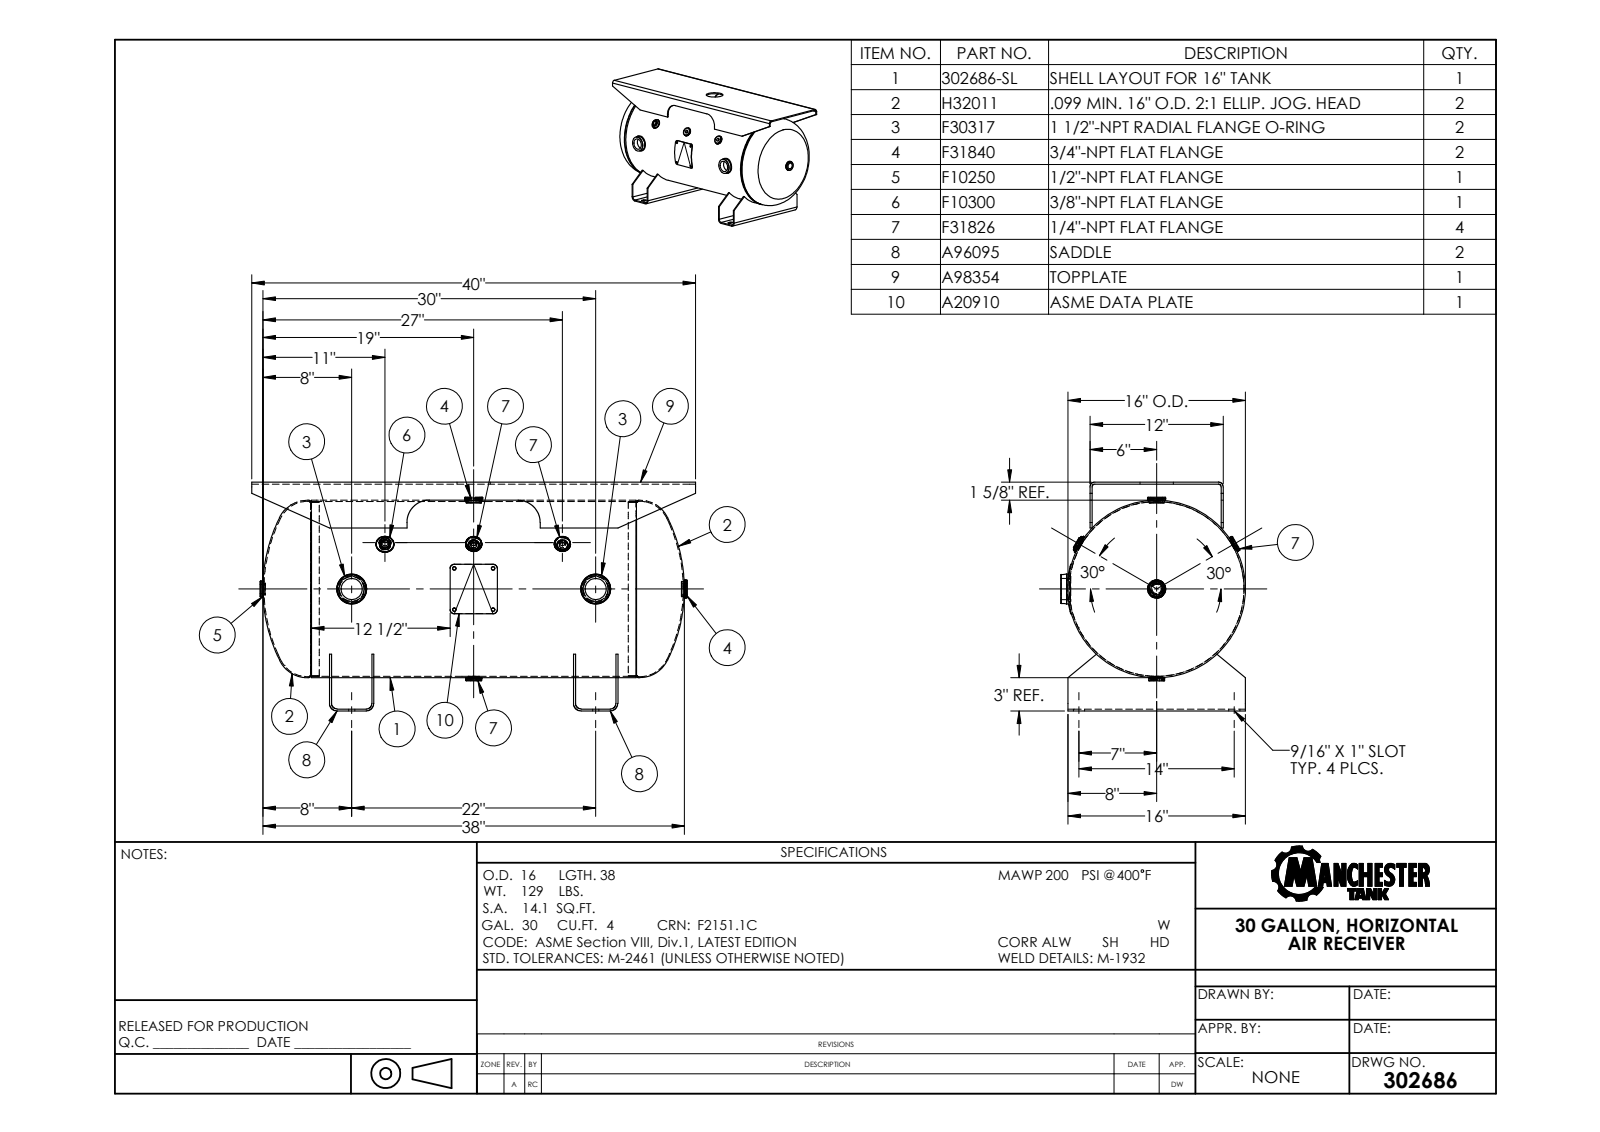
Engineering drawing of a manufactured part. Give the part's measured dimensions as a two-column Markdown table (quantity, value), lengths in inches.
| quantity | value |
| --- | --- |
| part name | 302686 |
| STEP written by | SolidWorks 2012 (CONFIG_CONTROL_DESIGN) |
| units | inches |
| bodies | 0 solids, 285 faces (102 planar, 89 cylindrical, 94 other) |
| overall size | 40 × 20.497 × 16.75 |
| round holes (diameter × count) | 0.54 × 4, 1 × 2, 1.05 × 2, 1.9 × 2, 0.675 × 1, 0.84 × 1, 1.063 × 1, 3 × 1, 15.758 × 1 |
| round bosses / shafts (diameter × count) | 1.5 × 4, 2.688 × 2, 2.266 × 2, 16 × 1, 15.74 × 1, 1.813 × 1, 1.63 × 1, 1.625 × 1 |
| partial cylindrical surfaces (radius × count) | 0.281 × 8, 0.281 × 6, 0.102 × 4, 0.094 × 2, 2.5 × 2, 8.06 × 1 |
| main face-to-face distances | 0.187, 0.179, 22, 3.821, 11.813, 4, 22.179, 21.821, 25.821, 3.642 |
| hole center spacings | 8, 16, 22 |
